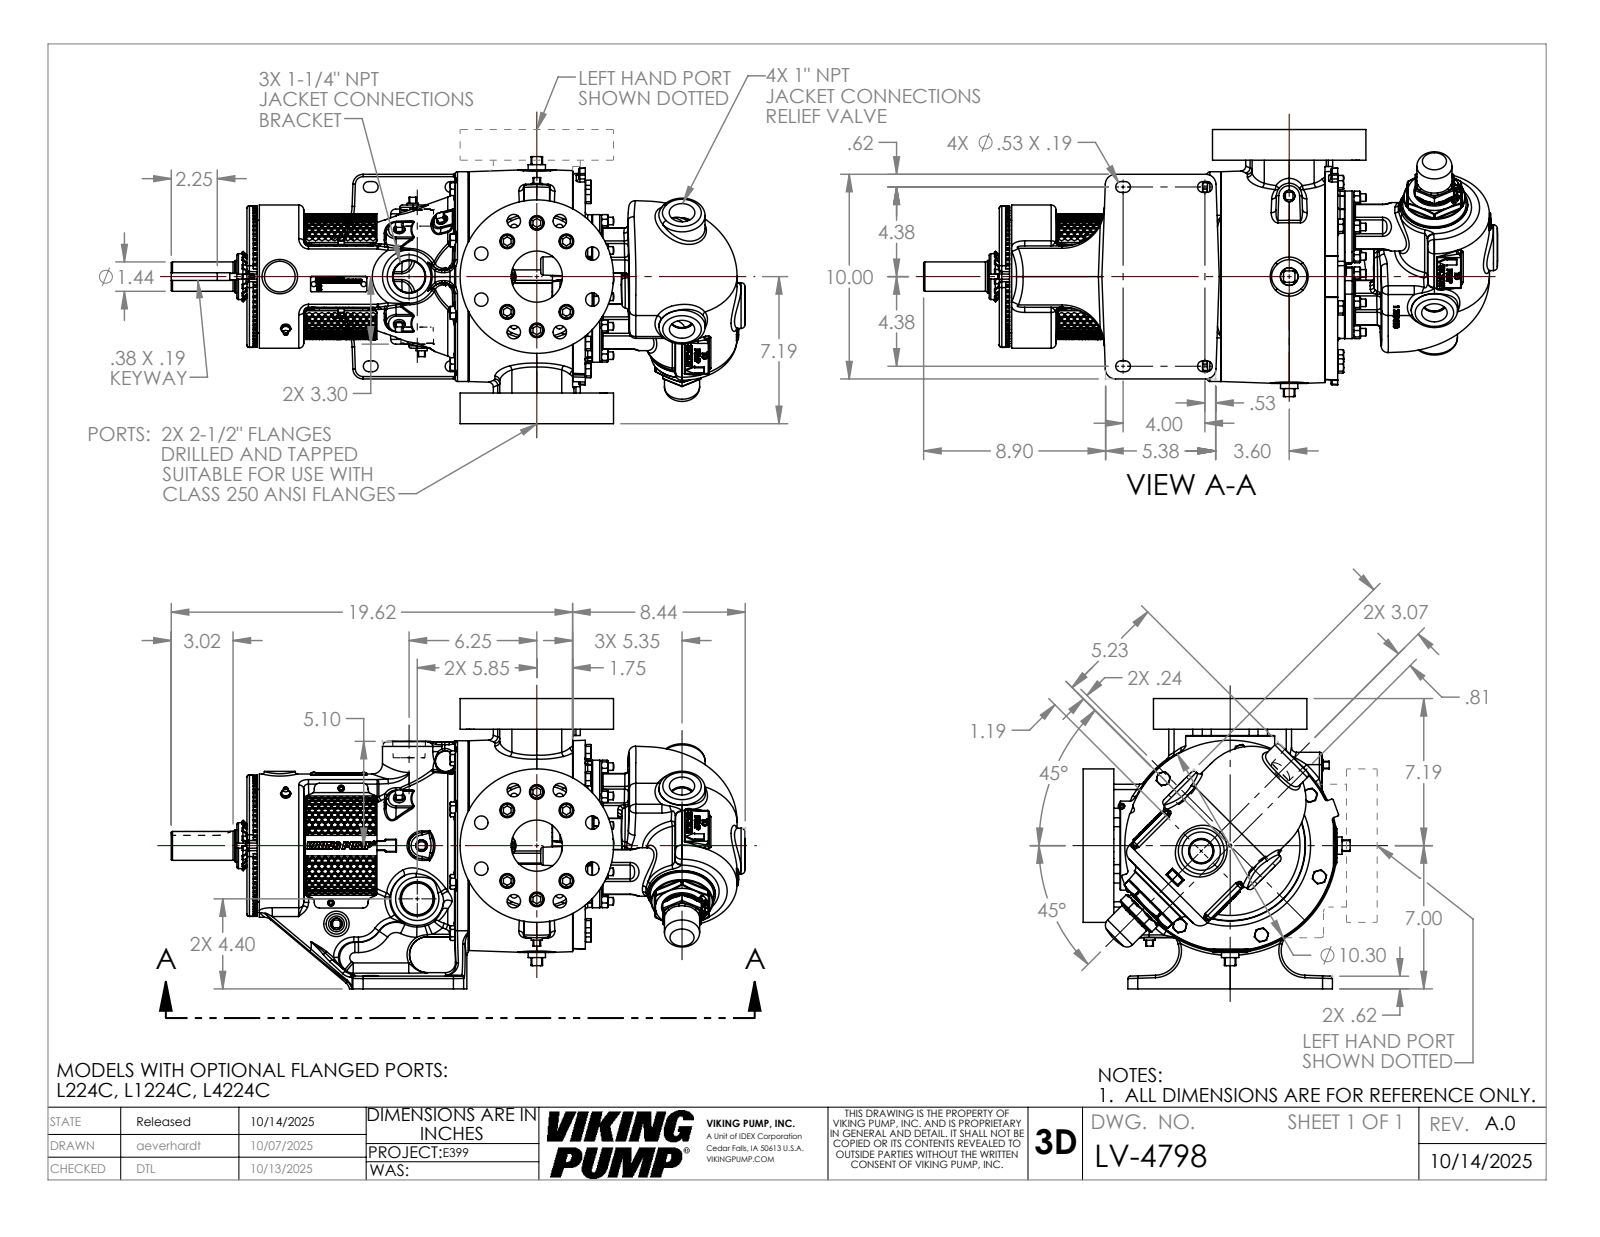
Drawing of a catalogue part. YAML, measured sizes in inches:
part_name: "LV-4798"
step_written_by: "SolidWorks 2024 (AUTOMOTIVE_DESIGN)"
units: inches
bodies: {solids: 1, faces: 5624, planar: 1838, cylindrical: 971, other: 2815}
overall_size: [28.059, 14.188, 13.053]
volume: 1243
surface_area: 1653
round_holes:
  - {diameter: 0.656, count: 16}
  - {diameter: 0.719, count: 12}
  - {diameter: 1.094, count: 8}
  - {diameter: 0.199, count: 6}
  - {diameter: 0.25, count: 6}
  - {diameter: 0.159, count: 3}
  - {diameter: 0.266, count: 2}
  - {diameter: 0.313, count: 2}
  - {diameter: 2.5, count: 2}
  - {diameter: 0.453, count: 1}
  - {diameter: 1.577, count: 1}
  - {diameter: 1.593, count: 1}
round_bosses_or_shafts:
  - {diameter: 0.66, count: 12}
  - {diameter: 0.625, count: 9}
  - {diameter: 0.369, count: 8}
  - {diameter: 0.625, count: 6}
  - {diameter: 3.5, count: 3}
  - {diameter: 0.437, count: 3}
  - {diameter: 0.312, count: 3}
  - {diameter: 7.5, count: 2}
partial_cylinders:
  - {radius: 0.063, count: 109}
  - {radius: 0.12, count: 82}
  - {radius: 0.069, count: 74}
  - {radius: 0.03, count: 34}
  - {radius: 0.5, count: 34}
  - {radius: 0.24, count: 16}
  - {radius: 1, count: 16}
  - {radius: 0.19, count: 14}
face_to_face_distances: [1.5, 14.187, 12.687, 2.25, 13.792, 3.537, 10.255, 2.75, 0.5, 2.143]
hole_center_spacings: [2.248, 3, 2.937, 5.428, 1.375, 1.041, 1.402, 2.18]
